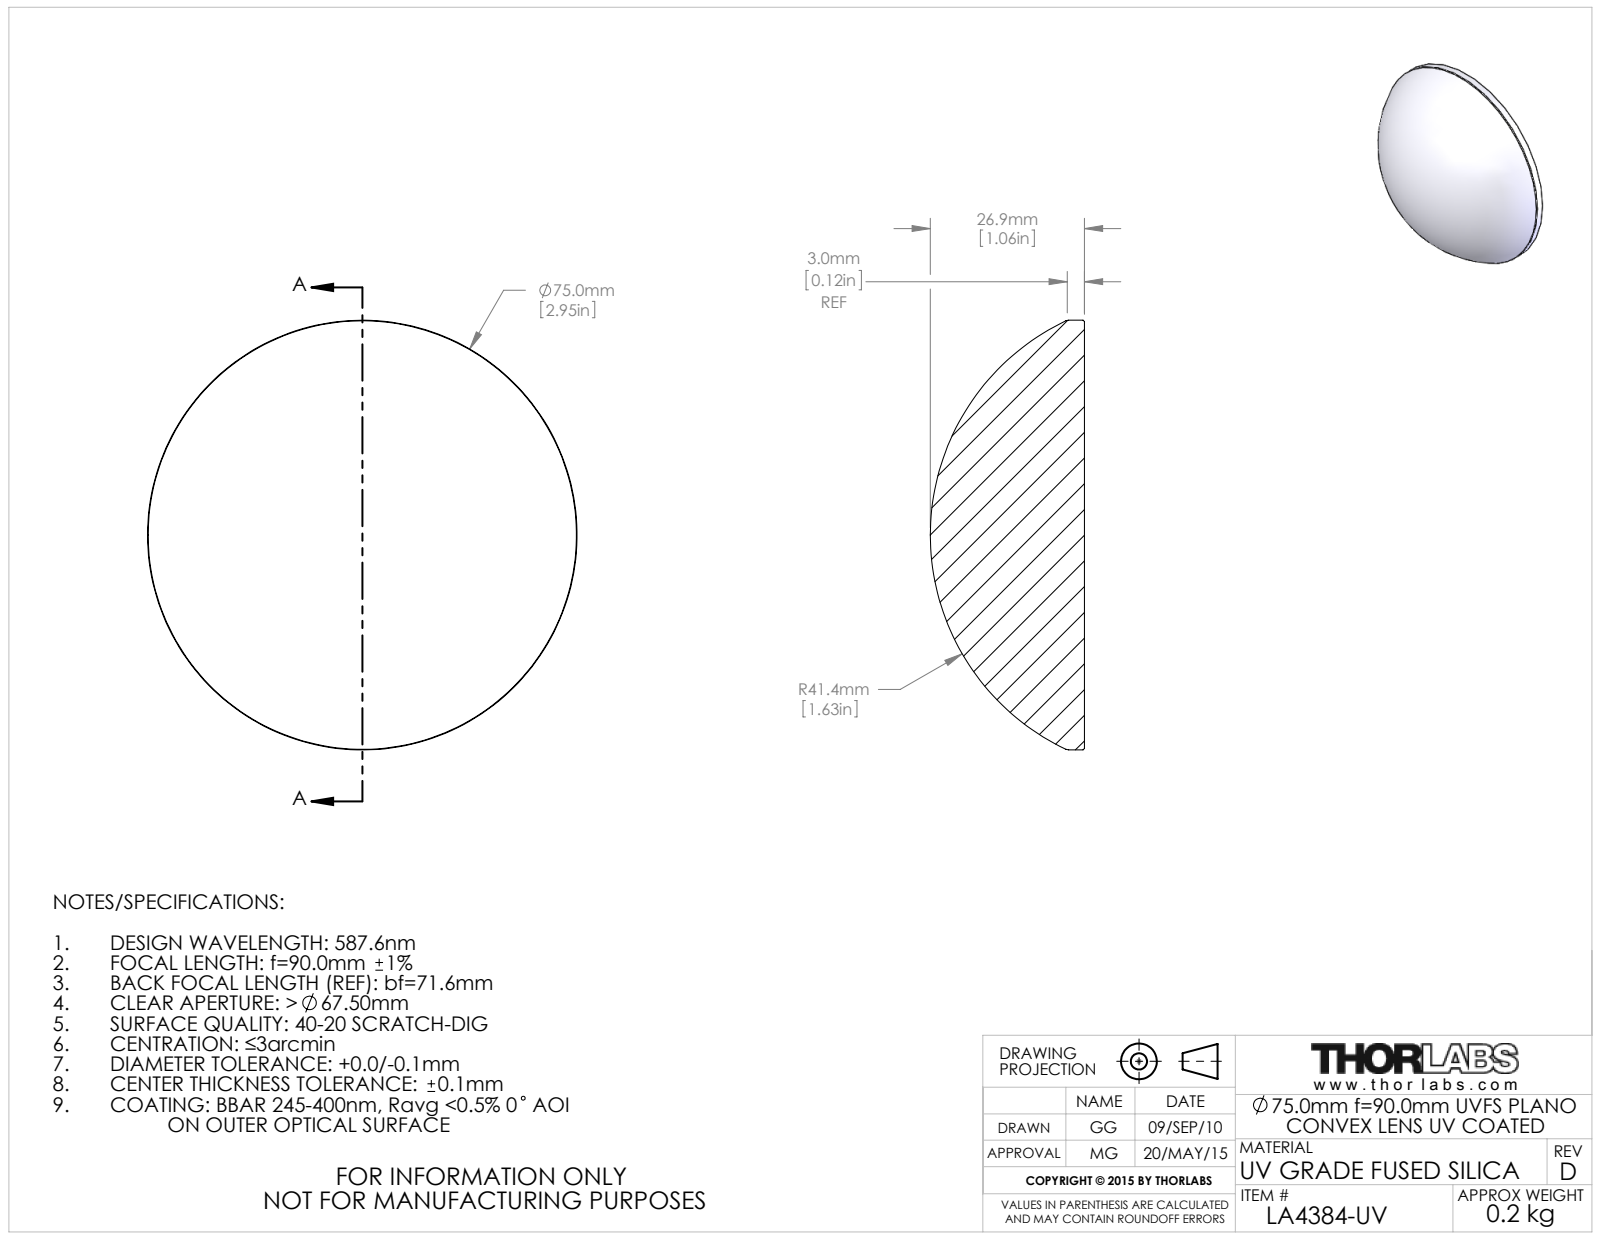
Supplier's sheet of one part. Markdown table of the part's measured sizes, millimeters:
| quantity | value |
| --- | --- |
| part name | 4302-E0W |
| STEP written by | SolidWorks 2014 (CONFIG_CONTROL_DESIGN) |
| units | millimeters |
| bodies | 1 solid, 9 faces (1 planar, 2 cylindrical, 6 other) |
| overall size | 75 × 75 × 26.9 |
| volume | 73 161 mm³ |
| surface area | 11 298 mm² |
| round bosses / shafts (diameter × count) | 75 × 1 |
